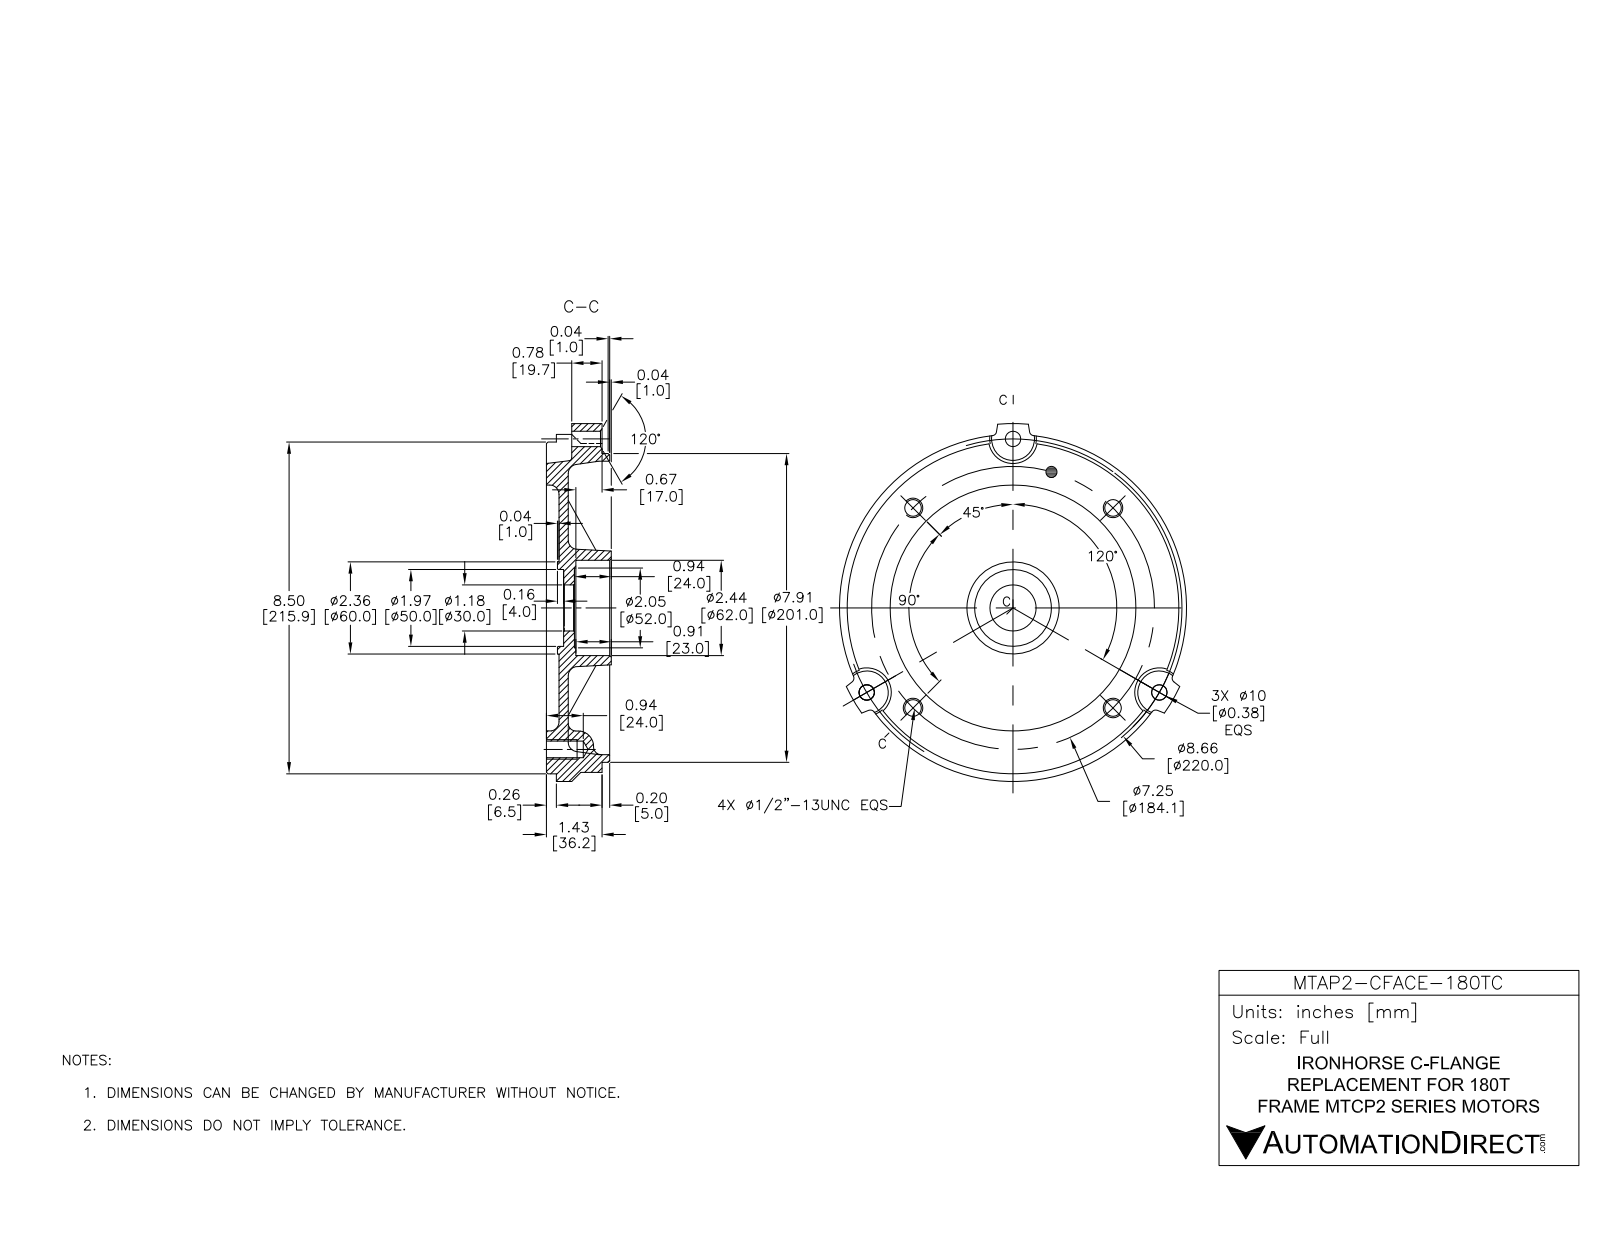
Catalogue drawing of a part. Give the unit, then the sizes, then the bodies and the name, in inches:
Units: inches
Overall size (bounding box): 9.171 × 8.894 × 1.661
Round holes (diameter × count): ⌀0.492 ×4, ⌀0.394 ×3, ⌀1.181 ×1, ⌀1.969 ×1, ⌀2.05 ×1, ⌀2.362 ×1, ⌀6.299 ×1, ⌀7.52 ×1
Round bosses / shafts (diameter × count): ⌀8.894 ×1, ⌀8.5 ×1, ⌀8.425 ×1, ⌀7.913 ×1
Partial cylindrical surfaces — rounded edges, fillets, slot ends (radius × count): R4.724 ×1
Main face-to-face distances: 0.559, 1.425, 0.866, 0.256, 0.303, 1.169, 1.622, 1.366, 1.063, 0.197
Hole centre spacings: 5.126, 3.625, 1.252, 3.113, 4.331, 4.876, 6.326, 7.25
Volume: 39.95 in³ · Surface area: 214.2 in²
Bodies: 1 solid, 114 faces (34 planar, 45 cylindrical, 35 other)
Part name (STEP PRODUCT): MTAP2-CFACE-180TC
STEP written by: SolidWorks 2017 (AUTOMOTIVE_DESIGN)
